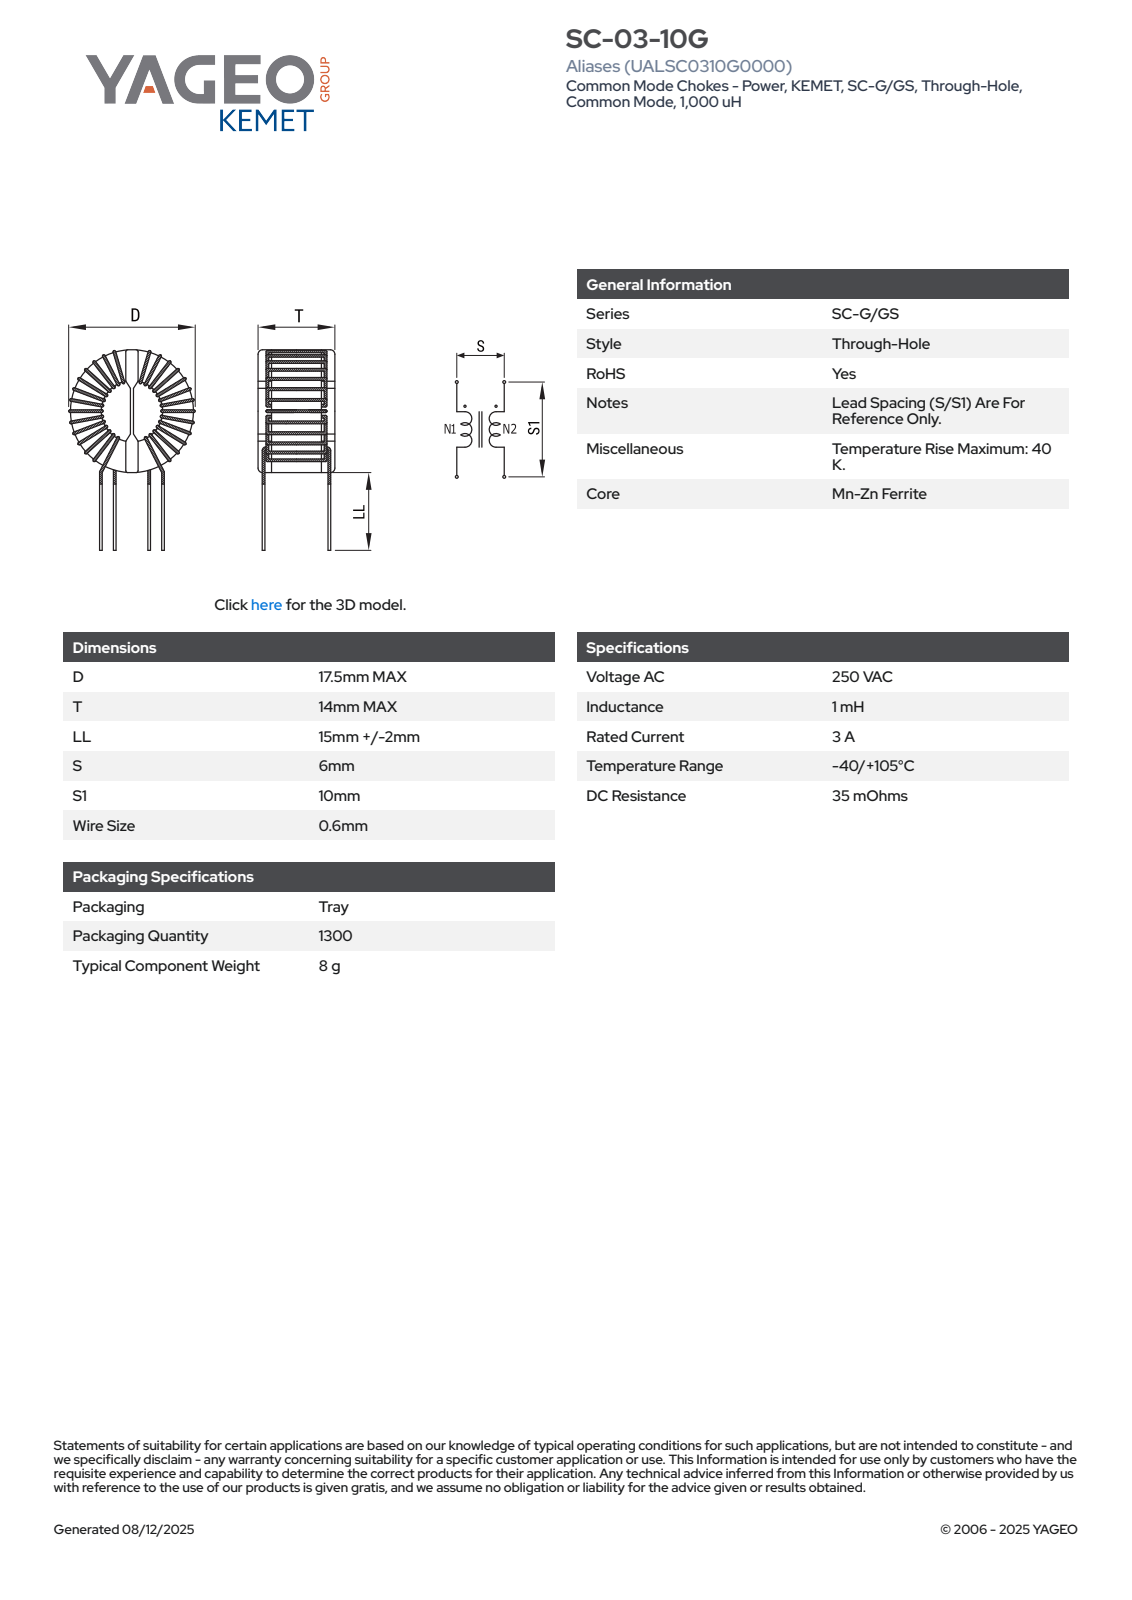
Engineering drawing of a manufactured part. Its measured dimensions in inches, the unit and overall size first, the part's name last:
Units: inches
Overall size (bounding box): 1.195 × 0.689 × 0.551
Round holes (diameter × count): ⌀0.299 ×1, ⌀0.504 ×1
Round bosses / shafts (diameter × count): ⌀0.024 ×8, ⌀0.537 ×1, ⌀0.504 ×1, ⌀0.5 ×1, ⌀0.285 ×1
Partial cylindrical surfaces — rounded edges, fillets, slot ends (radius × count): R0.012 ×18, R0.091 ×1, R0.126 ×1, R0.144 ×1, R0.269 ×1, R0.344 ×1
Main face-to-face distances: 0.047, 0.079, 0.321, 0.069, 0.327, 0.258, 0.126, 0.063, 0.031, 0.022
Volume: 0.146 in³ · Surface area: 5.098 in²
Bodies: 4 solids, 251 faces (108 planar, 67 cylindrical, 76 other)
Part name (STEP PRODUCT): SC-03-10G
STEP written by: SolidWorks 2018 (AUTOMOTIVE_DESIGN)
